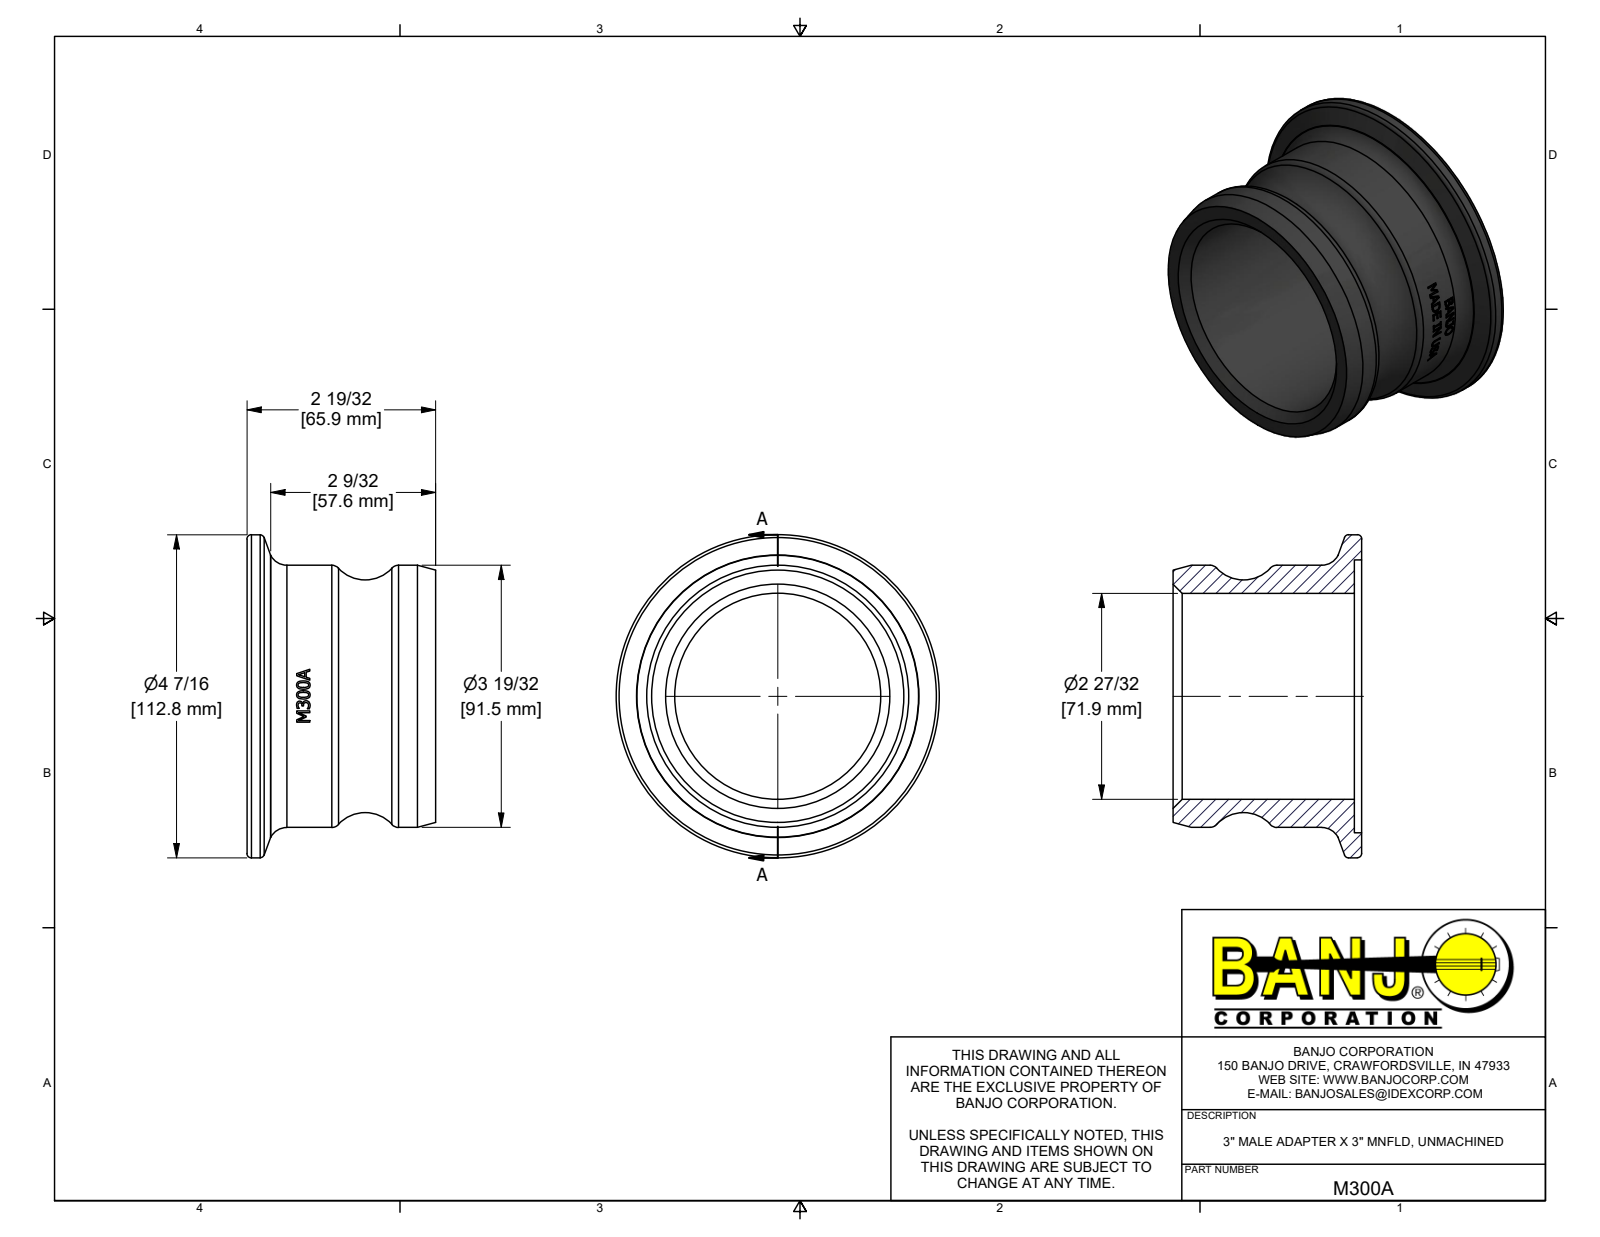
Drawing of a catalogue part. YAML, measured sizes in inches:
part_name: "M300A; M300AX"
step_written_by: "Autodesk Inventor 2019 (AUTOMOTIVE_DESIGN)"
units: inches
bodies: {solids: 1, faces: 311, planar: 158, cylindrical: 34, other: 119}
overall_size: [4.44, 4.44, 2.586]
volume: 9.837
surface_area: 68.74
round_holes:
  - {diameter: 2.83, count: 1}
  - {diameter: 3.75, count: 1}
round_bosses_or_shafts:
  - {diameter: 4.44, count: 1}
  - {diameter: 3.602, count: 1}
partial_cylinders:
  - {radius: 1.771, count: 1}
face_to_face_distances: [0.1, 2.586, 2.486, 0.15, 0.113, 0.247, 0.822, 0.722, 1.764, 0.019]
